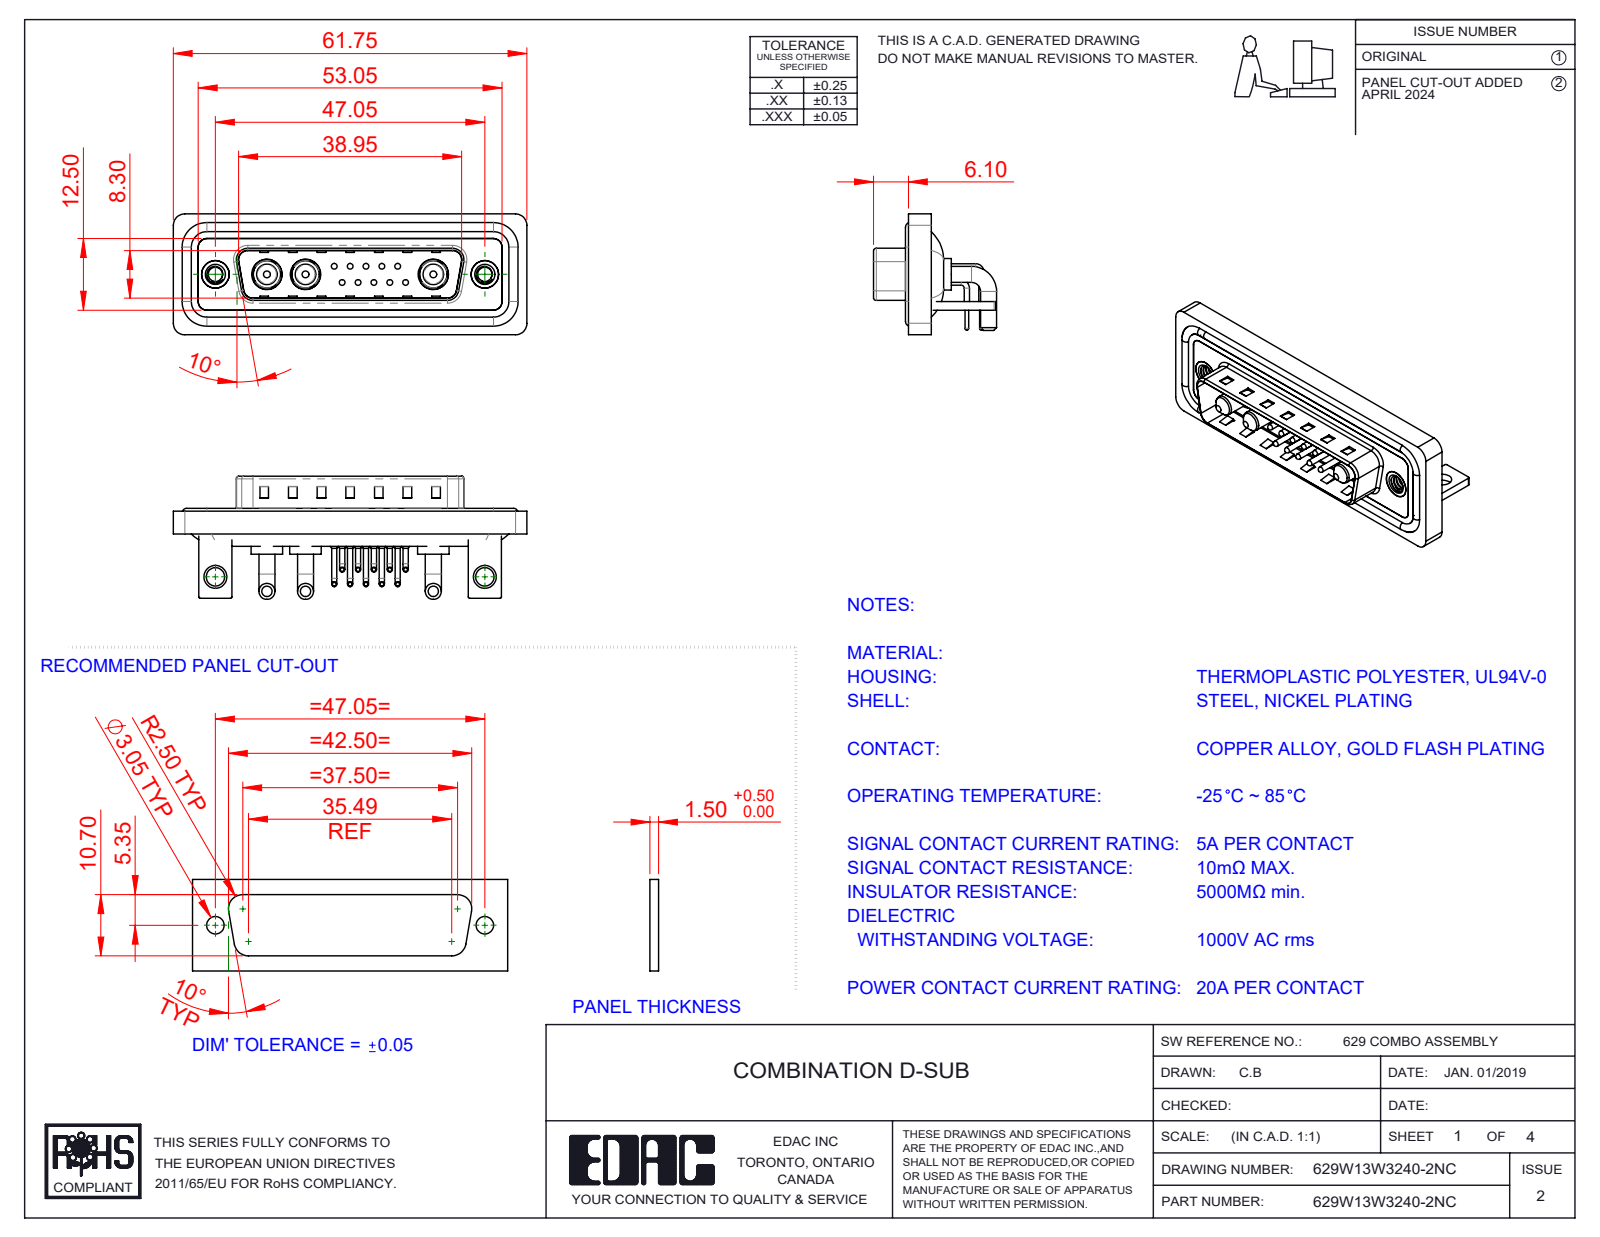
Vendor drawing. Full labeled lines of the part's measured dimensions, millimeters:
Part name (STEP PRODUCT): 629Combo Threaded Rivet_B; 629Combo Housing_13W3; 629Combo Contact Row 2; 629W13W3240-2NC (+6 more)
STEP written by: SolidWorks 2023 (CONFIG_CONTROL_DESIGN)
Units: millimetres
Bodies: 25 solids, 1750 faces (899 planar, 629 cylindrical, 222 other)
Overall size (bounding box): 61.75 × 21.5 × 21.1
Volume: 7 882 mm³ · Surface area: 13 084 mm²
Round holes (diameter × count): ⌀0.75 ×10, ⌀1.6 ×10, ⌀2 ×10, ⌀4.85 ×3, ⌀5.3 ×3, ⌀2.5 ×2, ⌀3.2 ×2, ⌀4 ×2, ⌀4.8 ×2, ⌀5 ×2
Round bosses / shafts (diameter × count): ⌀0.9 ×20, ⌀1.5 ×10, ⌀1 ×10, ⌀0.65 ×10, ⌀2.8 ×6, ⌀1.6 ×4, ⌀5.5 ×3, ⌀5.2 ×3
Partial cylindrical surfaces — rounded edges, fillets, slot ends (radius × count): R2 ×19, R1.5 ×18, R0.25 ×16, R1.01 ×10, R0.5 ×9, R1.6 ×8, R0.6 ×4, R0.65 ×4
Main face-to-face distances: 0.4, 1.5, 0.8, 2.9, 2.1, 1.1, 4.1, 1.6, 3.7, 4.5
Hole centre spacings: 3.16, 2.77, 5.04, 5.54, 7.49, 5.03, 8.31, 10.11
